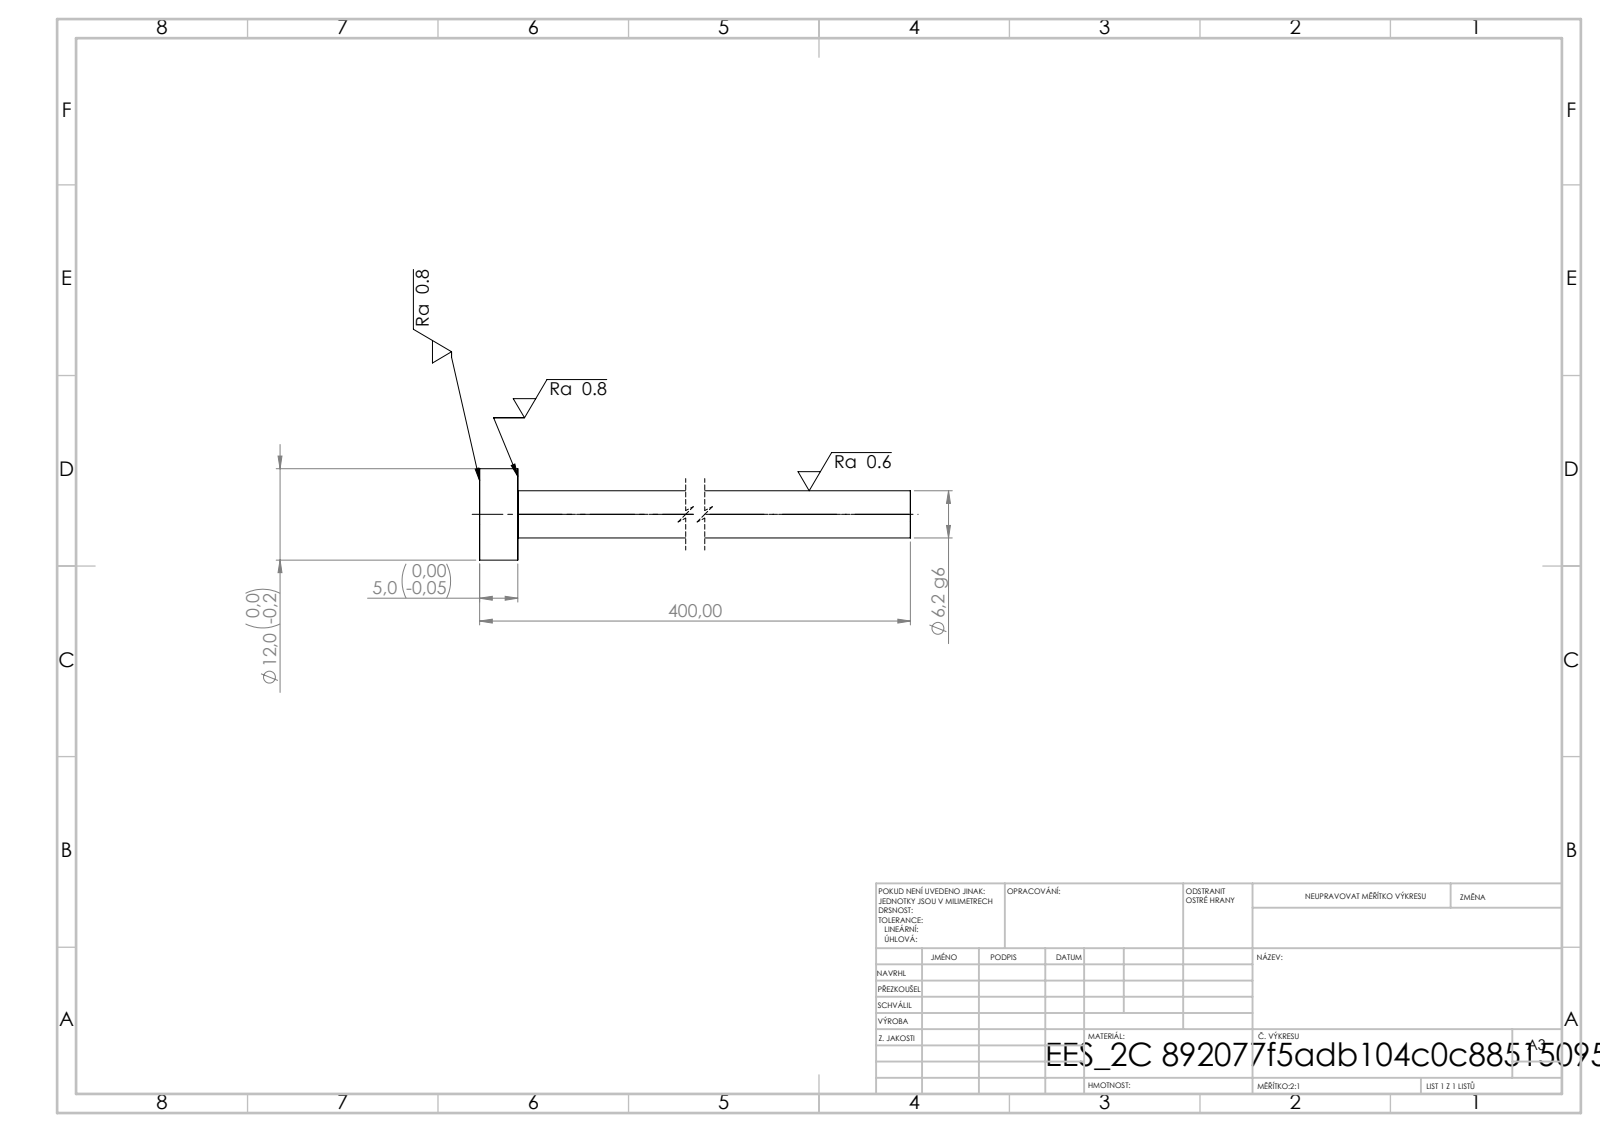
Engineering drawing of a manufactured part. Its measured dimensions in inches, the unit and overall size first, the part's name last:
Units: inches
Overall size (bounding box): 15.748 × 0.472 × 0.472
Round bosses / shafts (diameter × count): ⌀0.472 ×1, ⌀0.244 ×1
Main face-to-face distances: 0.197, 15.748, 15.551
Volume: 0.762 in³ · Surface area: 12.57 in²
Bodies: 1 solid, 7 faces (3 planar, 4 cylindrical, 0 other)
STEP written by: SolidWorks 2019 (CONFIG_CONTROL_DESIGN)
